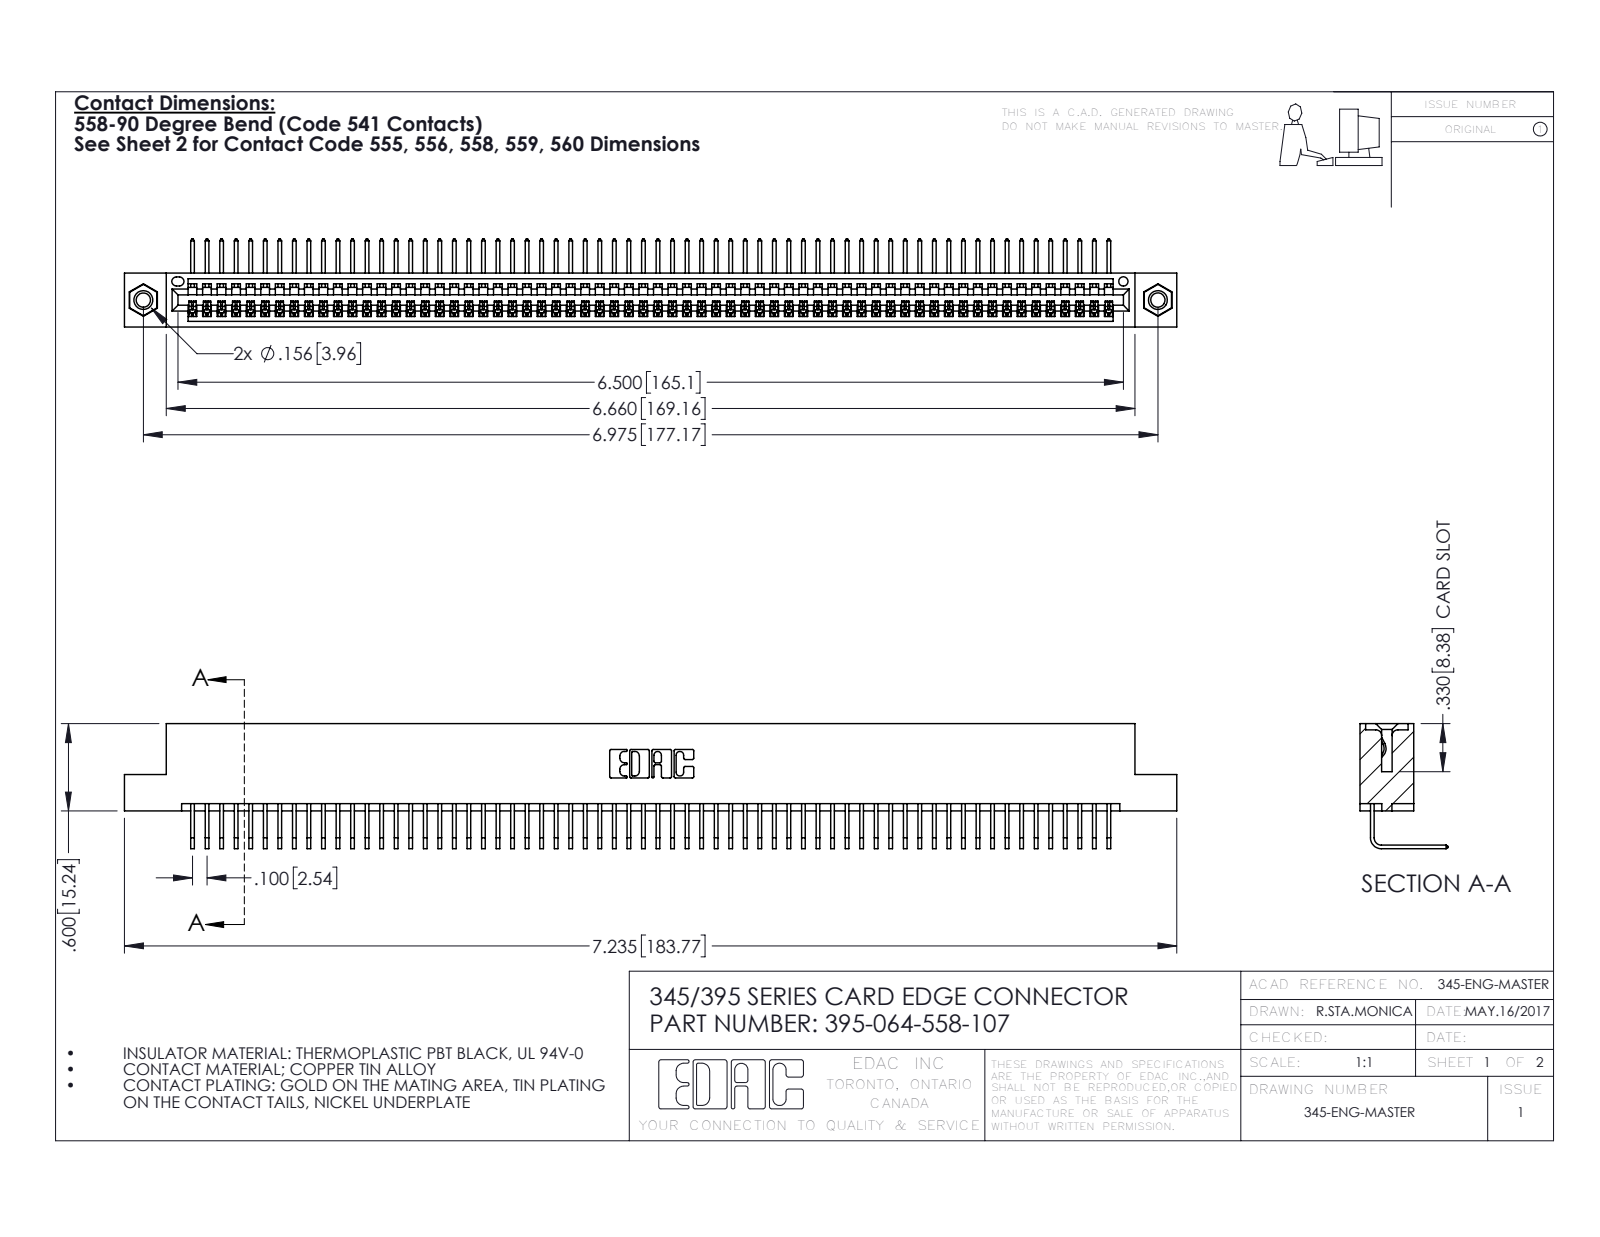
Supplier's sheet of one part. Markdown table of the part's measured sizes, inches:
| quantity | value |
| --- | --- |
| part name | 345-292-001_558 Tail - 2; 395-064-558-107; 345 Part_Flush Mounting Lugs - 0.156 Dia-TI; 345-250-001_345-250-005-103 |
| STEP written by | SolidWorks 2016 (CONFIG_CONTROL_DESIGN) |
| units | inches |
| bodies | 67 solids, 4026 faces (2800 planar, 1210 cylindrical, 16 other) |
| overall size | 7.235 × 0.859 × 0.605 |
| volume | 1.088 in³ |
| surface area | 39.19 in² |
| round holes (diameter × count) | 0.098 × 2, 0.125 × 2, 0.156 × 2, 0.064 × 1 |
| round bosses / shafts (diameter × count) | 0.155 × 2 |
| partial cylindrical surfaces (radius × count) | 0.006 × 128, 0.01 × 22, 0.007 × 6, 0.031 × 6, 0.026 × 3, 0.031 × 2, 0.04 × 2, 0.014 × 1 |
| main face-to-face distances | 0.072, 0.298, 0.37, 0.2, 0.098, 0.272, 0.025, 0.225, 0.149, 0.072 |
| hole center spacings | 0.27, 6.739, 6.975 |
